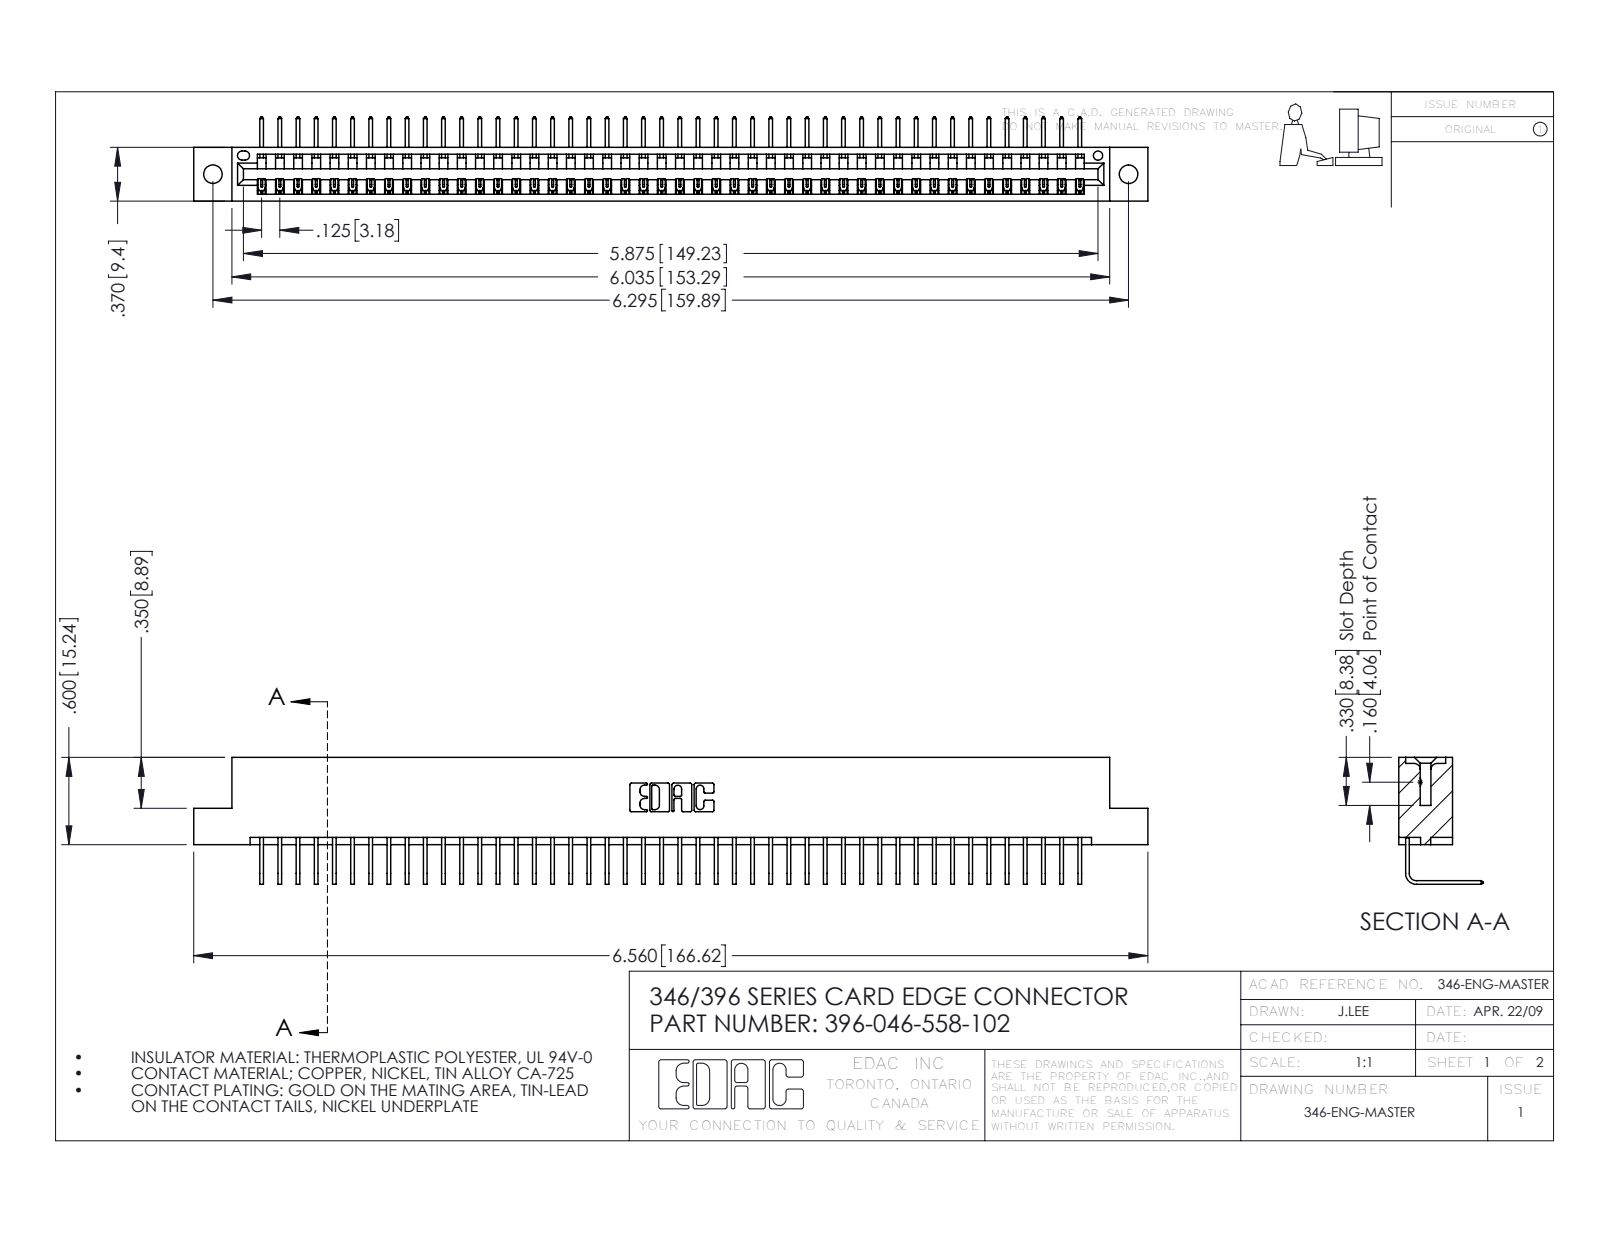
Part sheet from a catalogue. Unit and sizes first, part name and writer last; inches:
Units: inches
Overall size (bounding box): 6.56 × 0.873 × 0.58
Round holes (diameter × count): ⌀0.128 ×2, ⌀0.064 ×1
Partial cylindrical surfaces — rounded edges, fillets, slot ends (radius × count): R0.006 ×92, R0.01 ×22, R0.007 ×6, R0.031 ×6, R0.026 ×3, R0.031 ×2, R0.04 ×2, R0.014 ×1
Main face-to-face distances: 0.322, 0.048, 0.37, 0.25, 0.298, 0.025, 0.072, 0.148, 0.222, 0.1
Hole centre spacings: 0.246, 6.086, 6.295
Volume: 0.982 in³ · Surface area: 32.24 in²
Bodies: 47 solids, 2882 faces (2008 planar, 874 cylindrical, 0 other)
Part name (STEP PRODUCT): 396-046-558-102; 345-292-001_558 Tail - 2; 346 Part_Flush Mounting Lugs - 0.128 Dia
STEP written by: SolidWorks 2016 (CONFIG_CONTROL_DESIGN)
